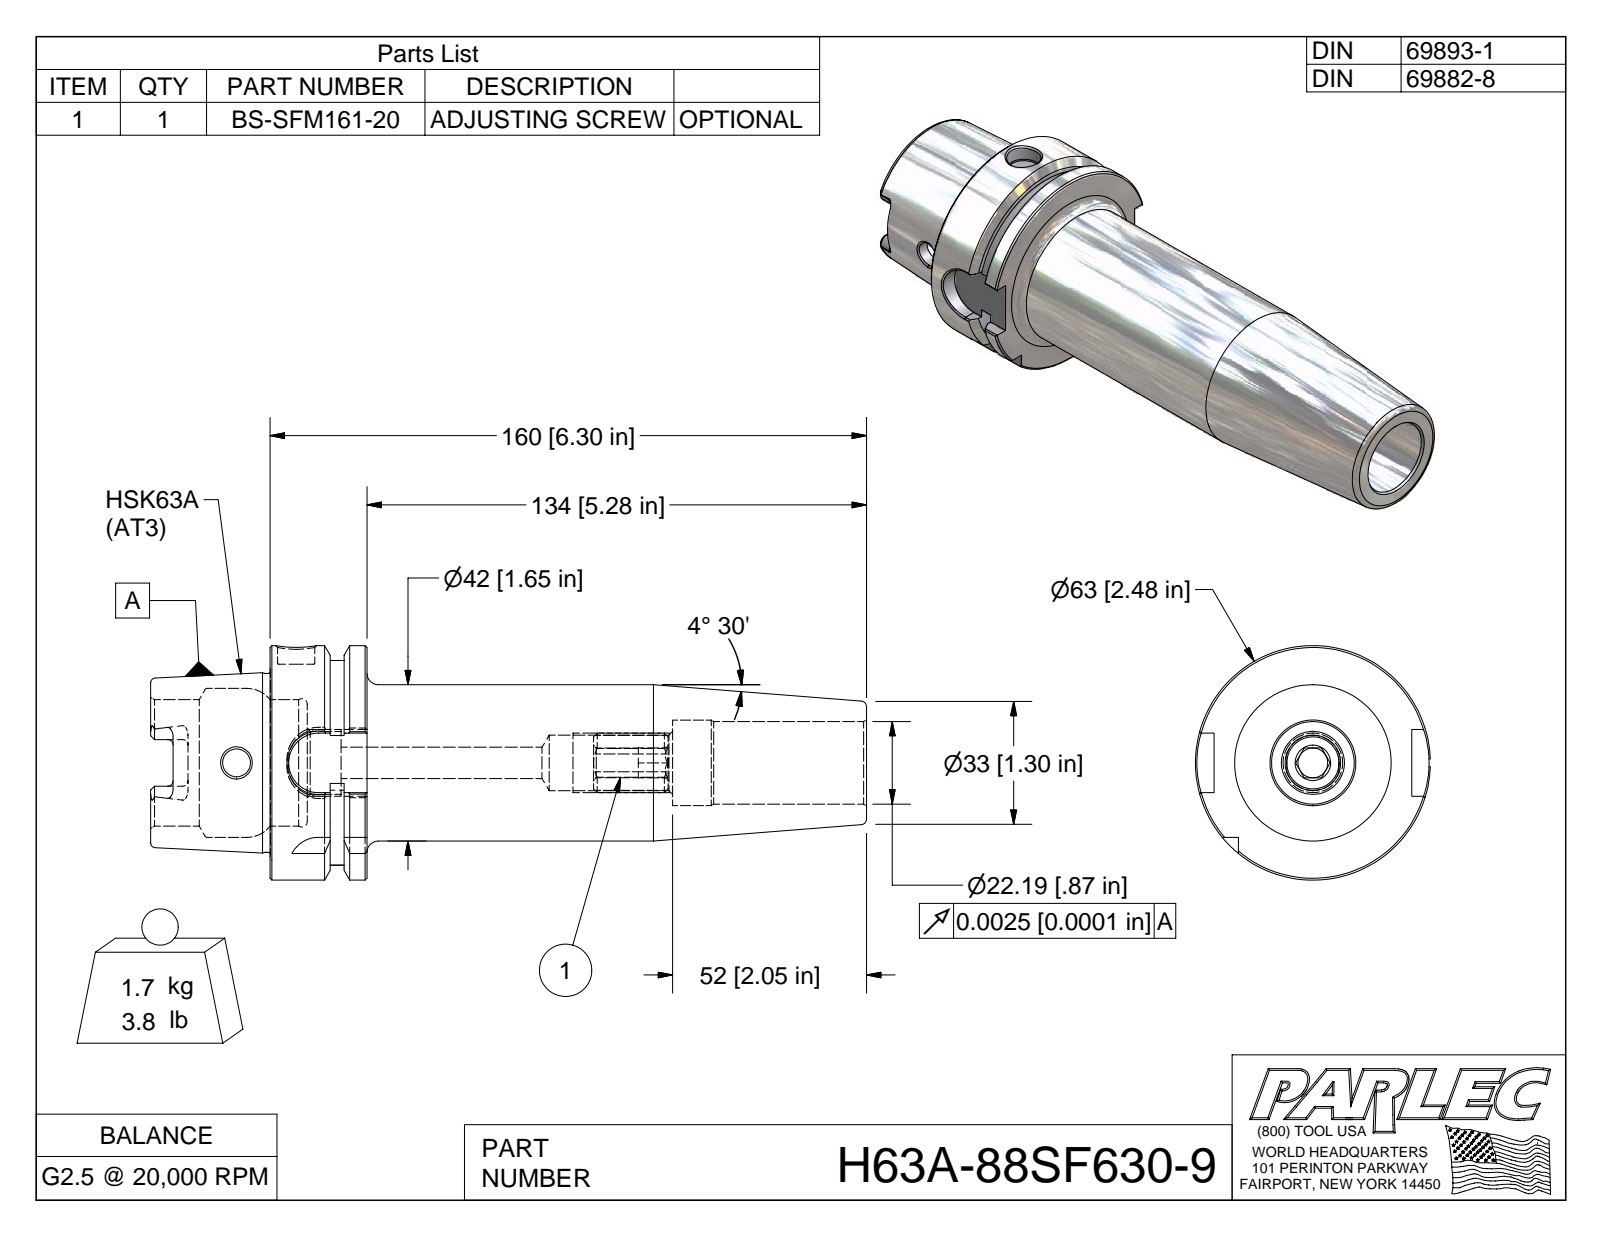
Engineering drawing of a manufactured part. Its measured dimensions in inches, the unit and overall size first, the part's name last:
Units: inches
Overall size (bounding box): 7.559 × 2.48 × 2.48
Round holes (diameter × count): ⌀0.295 ×1, ⌀0.394 ×1, ⌀0.666 ×1, ⌀0.874 ×1, ⌀0.904 ×1, ⌀1.339 ×1, ⌀1.575 ×1
Round bosses / shafts (diameter × count): ⌀2.48 ×1, ⌀1.891 ×1, ⌀1.654 ×1
Partial cylindrical surfaces — rounded edges, fillets, slot ends (radius × count): R0.059 ×6, R0.315 ×5, R0.113 ×4, R1.083 ×1
Main face-to-face distances: 1.024, 0.241, 0.389, 0.394, 0.63, 1.26, 1.654, 2.283, 5.276, 1.894
Volume: 13.76 in³ · Surface area: 72.24 in²
Bodies: 2 solids, 157 faces (58 planar, 35 cylindrical, 64 other)
Part name (STEP PRODUCT): H63A-88SF630-9; H63A-88SF630-9-1; BS-SFM161-20
STEP written by: Autodesk Inventor 2009 (AUTOMOTIVE_DESIGN)
